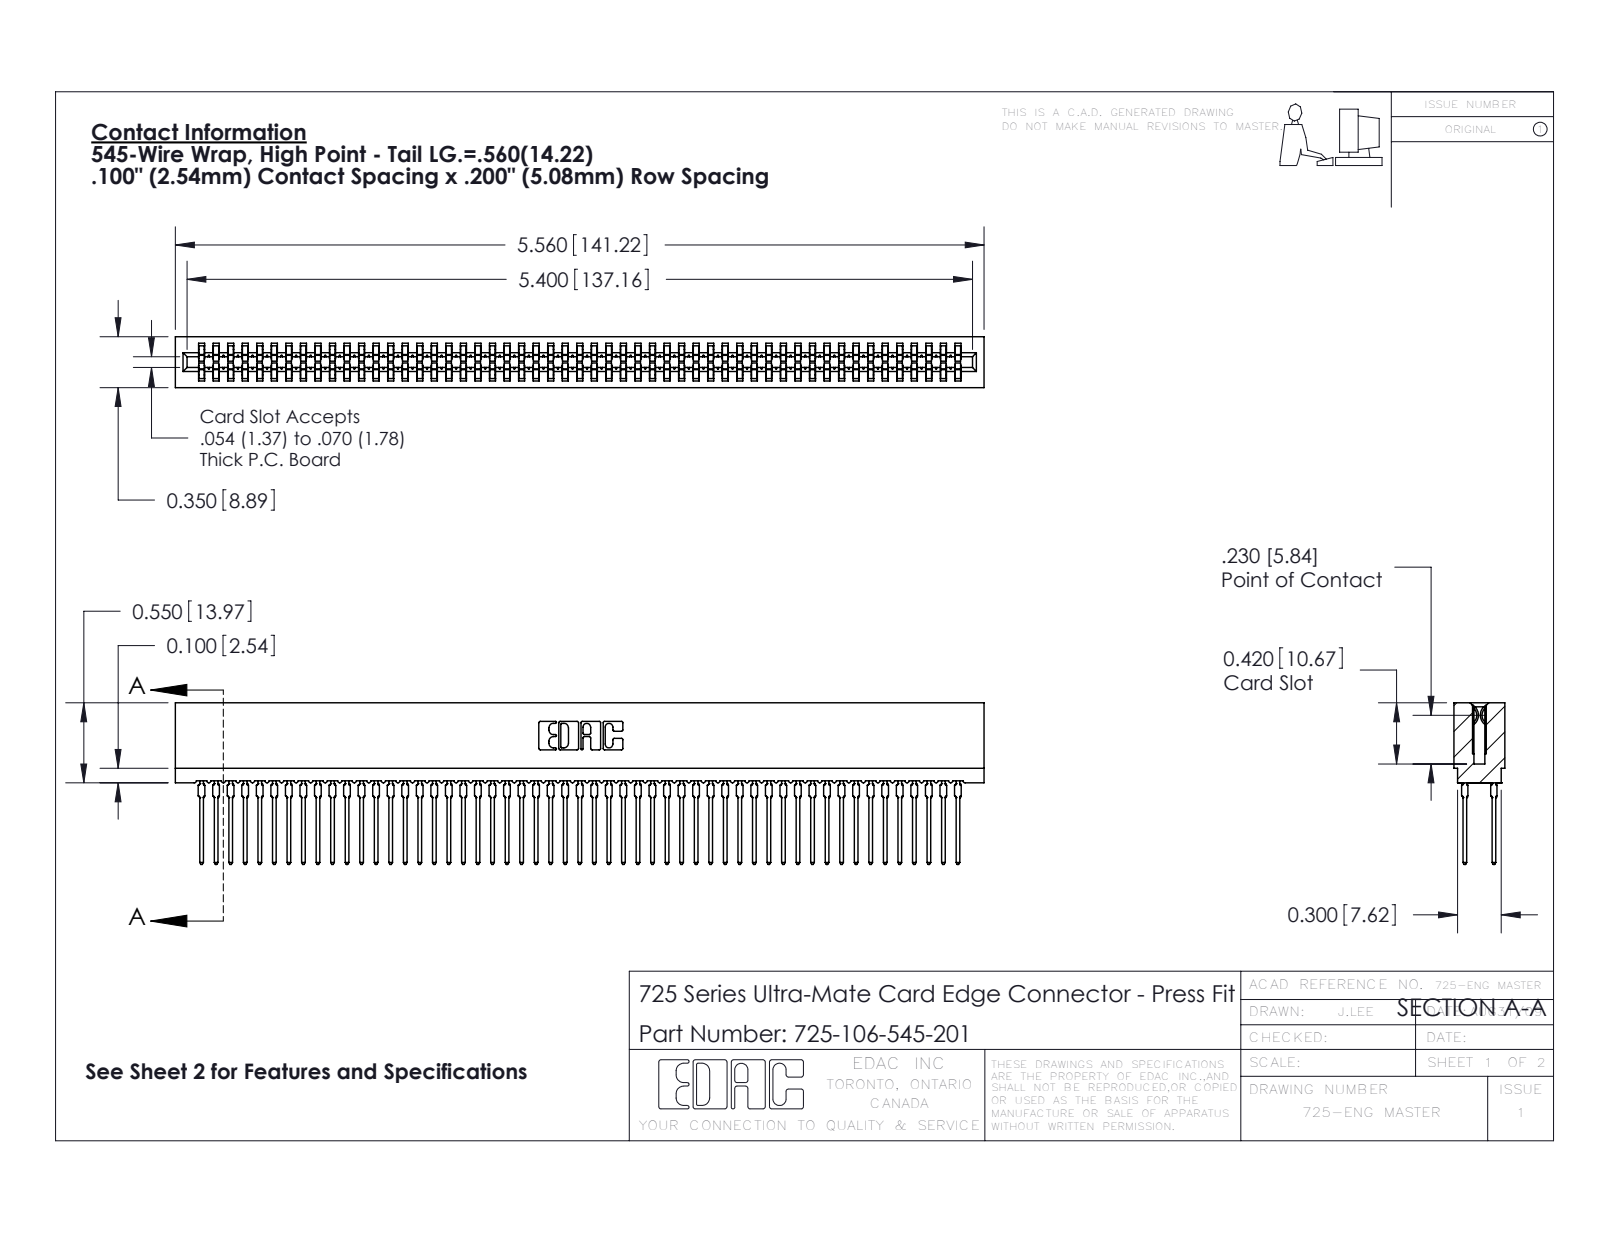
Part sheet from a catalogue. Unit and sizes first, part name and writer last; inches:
Units: inches
Overall size (bounding box): 5.56 × 1.11 × 0.35
Partial cylindrical surfaces — rounded edges, fillets, slot ends (radius × count): R0.021 ×212, R0.015 ×106, R0.01 ×22, R0.005 ×8, R0.011 ×8, R0.007 ×6, R0.031 ×6, R0.026 ×3
Main face-to-face distances: 0.063, 0.287, 0.2, 0.35, 0.212, 0.138, 0.076, 0.149, 0.087, 0.263
Volume: 0.703 in³ · Surface area: 40.57 in²
Bodies: 107 solids, 9582 faces (4931 planar, 1895 cylindrical, 2756 other)
Part name (STEP PRODUCT): 725-106-545-201; 745-292-001_545; 725 Part_Insulator Option - 01
STEP written by: SolidWorks 2016 (CONFIG_CONTROL_DESIGN)
